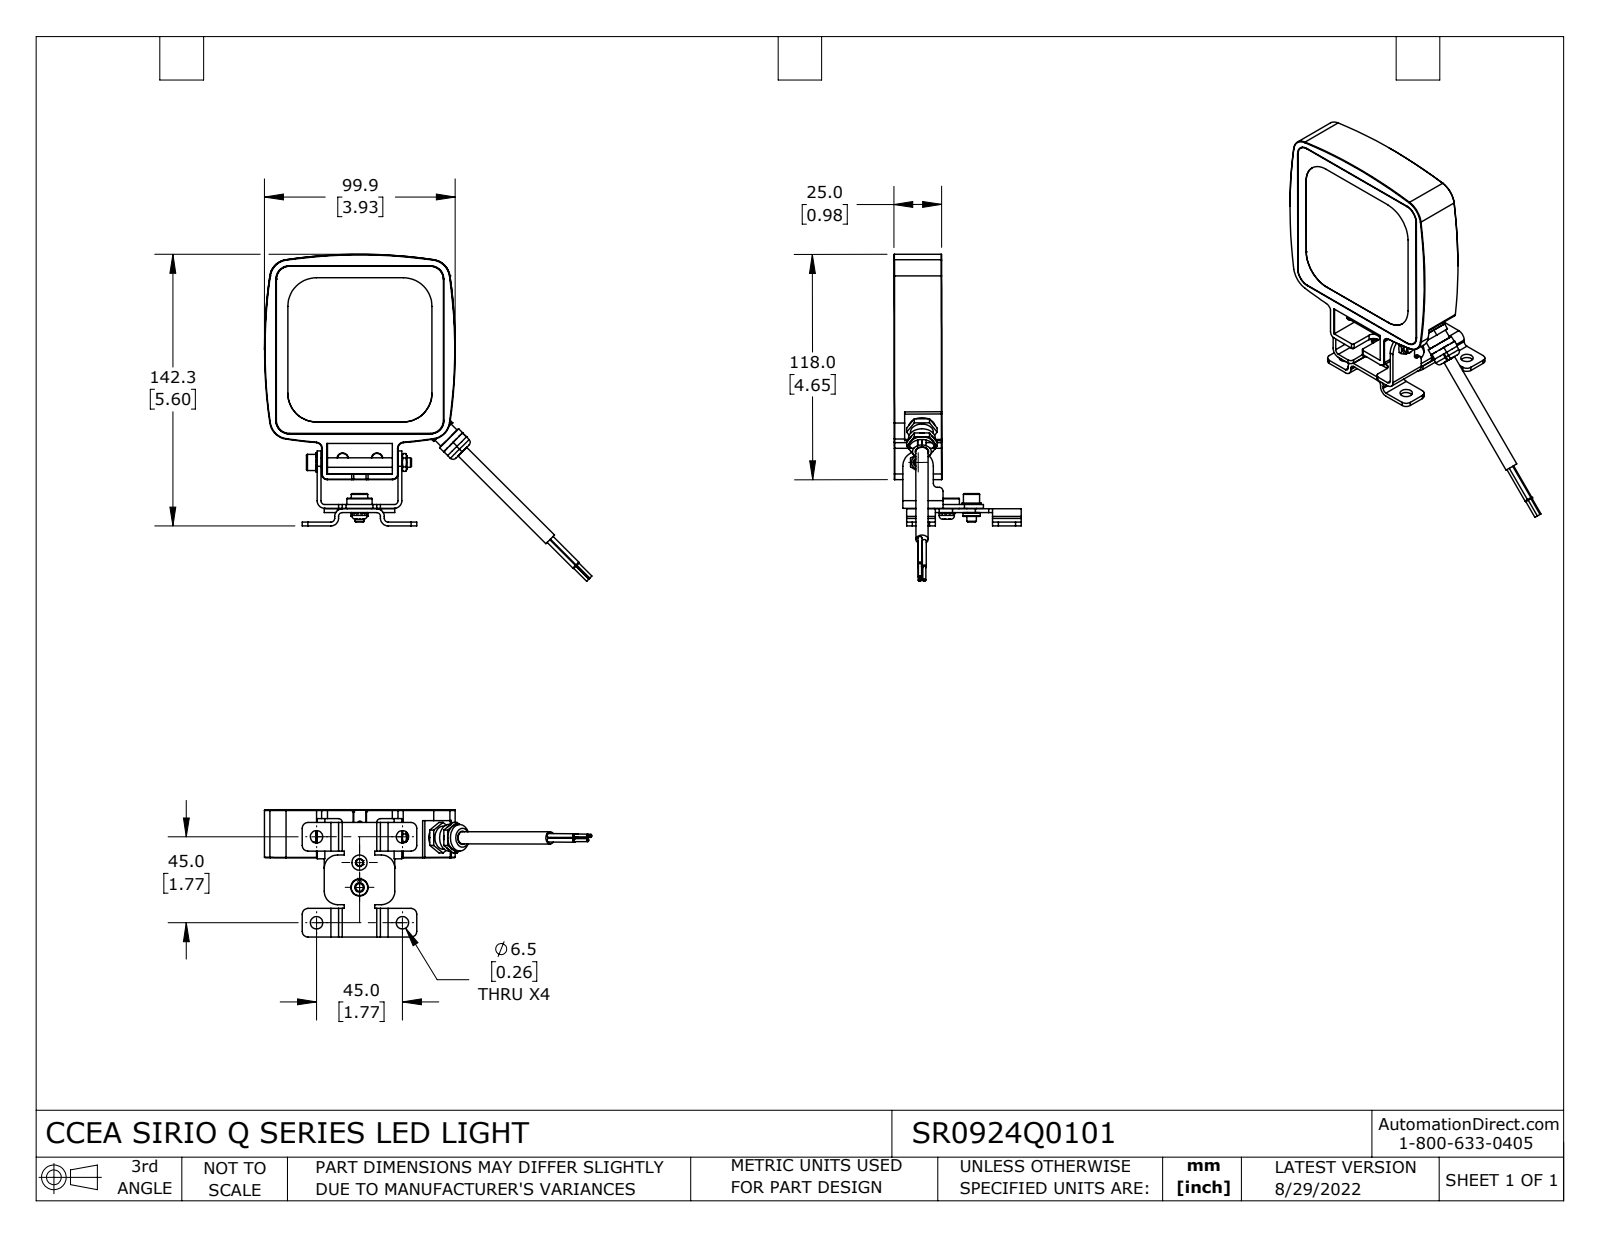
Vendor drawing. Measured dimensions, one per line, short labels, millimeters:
name: SR0924Q0101
written by: SolidWorks 2021 (CONFIG_CONTROL_DESIGN)
unit: mm
bodies: 2 solids, 776 faces (331 planar, 324 cylindrical, 121 other)
size: 171.5 × 171.2 × 66.6
volume: 155 700 mm³; area: 71 290 mm²
holes: 4× ⌀2.5, 4× ⌀6.5, 3× ⌀1.1, 3× ⌀5.5, 2× ⌀7, 1× ⌀3.3, 1× ⌀4.3, 1× ⌀5, 1× ⌀5.3, 1× ⌀9.4, 1× ⌀13.5
bosses: 6× ⌀1, 4× ⌀2.1, 3× ⌀1.7, 3× ⌀1.6, 2× ⌀8.5, 2× ⌀5, 2× ⌀2, 1× ⌀14
rounds: 22× R0.1, 22× R0.2, 22× R2, 12× R3, 8× R7, 6× R4, 6× R10, 5× R5
face distances: 4, 20.9, 24.9, 2, 3.1, 17.8, 21.8, 4.1, 14.4, 18.4
hole spacings: 45, 26.2, 38.7, 63.7, 1.5, 1.5, 1.7, 1.7
